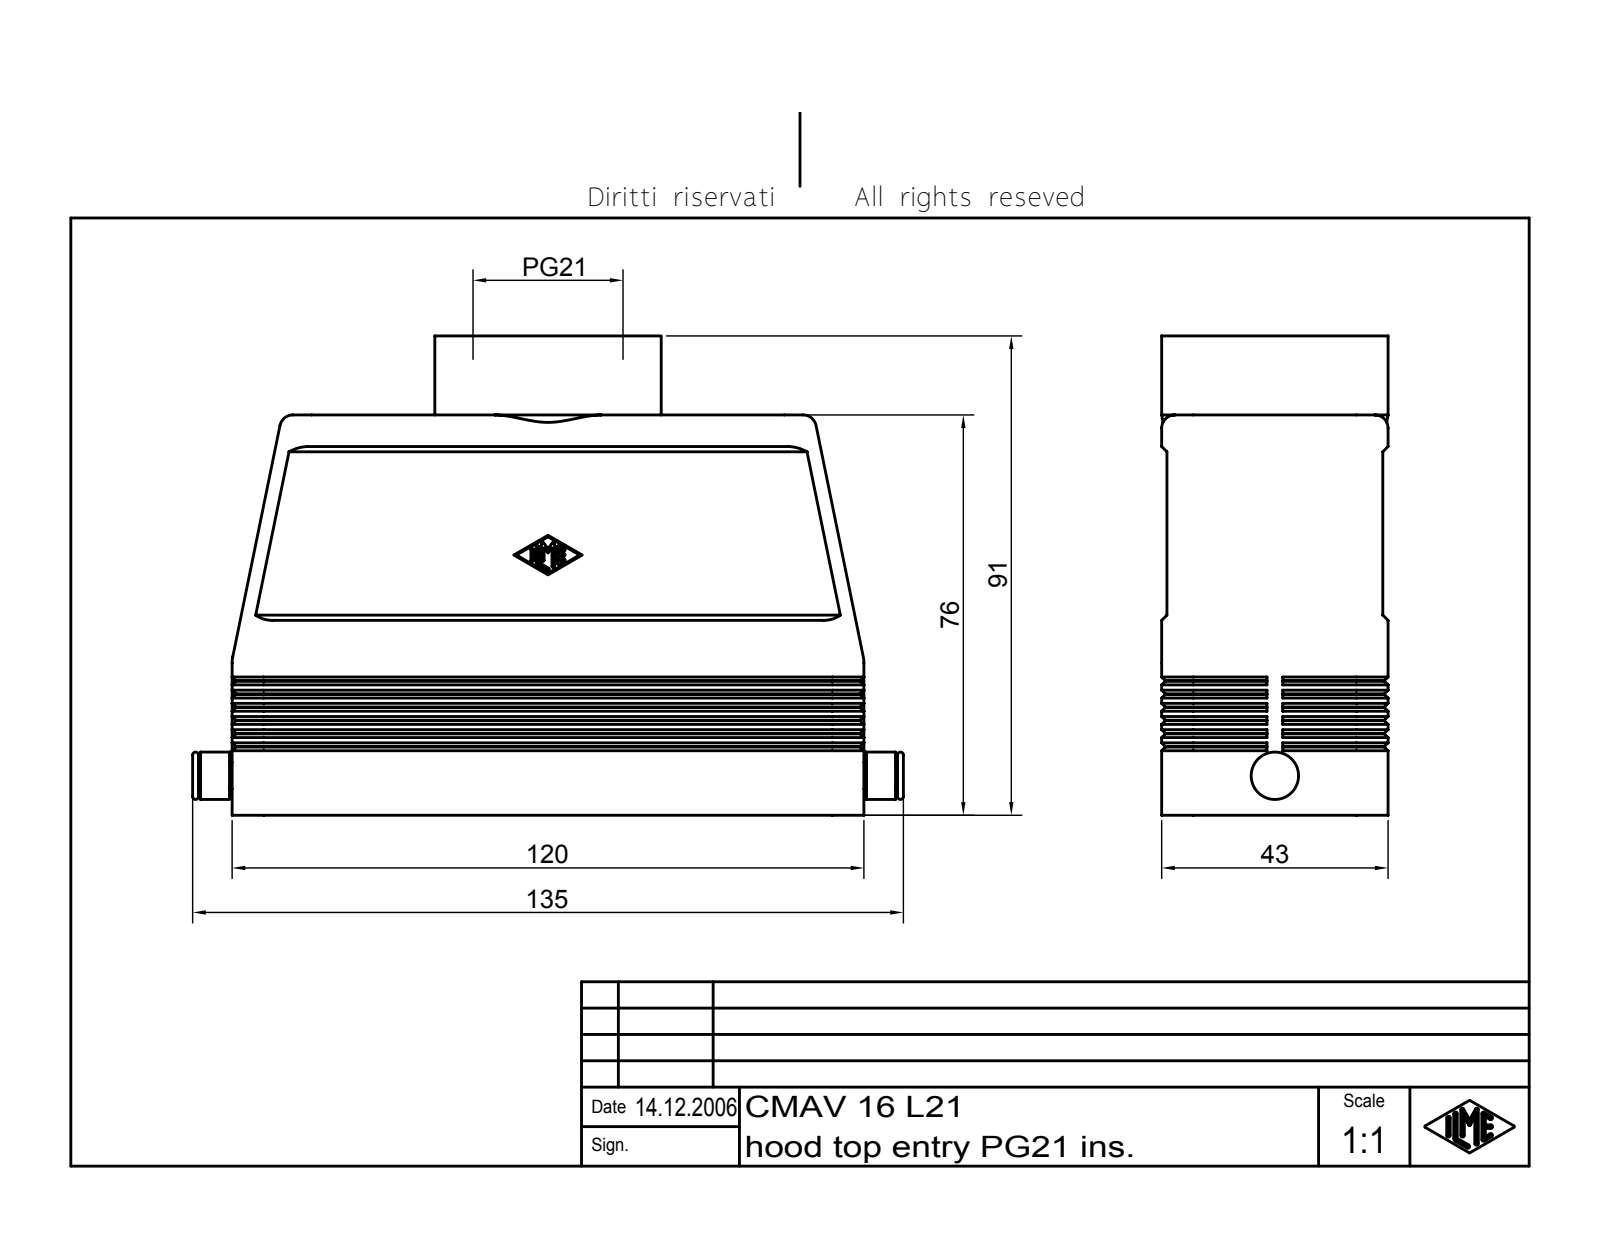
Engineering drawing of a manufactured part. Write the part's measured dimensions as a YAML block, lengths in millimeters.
part_name: "CH Tüllengehäuse für einen Einsatz Teil 6"
step_written_by: "Autodesk Inventor 7 (AUTOMOTIVE_DESIGN)"
units: millimeters
bodies: {solids: 1, faces: 525, planar: 193, cylindrical: 130, other: 202}
overall_size: [135, 91, 43]
volume: 96883
surface_area: 57879
round_holes:
  - {diameter: 24.78, count: 1}
  - {diameter: 26.78, count: 1}
round_bosses_or_shafts:
  - {diameter: 43, count: 1}
  - {diameter: 25.78, count: 1}
  - {diameter: 9, count: 1}
  - {diameter: 5, count: 1}
partial_cylinders:
  - {radius: 0.25, count: 14}
  - {radius: 6, count: 10}
  - {radius: 2, count: 4}
  - {radius: 2.5, count: 4}
  - {radius: 3, count: 4}
  - {radius: 5.3, count: 2}
face_to_face_distances: [3, 37, 40, 1, 2, 42, 39, 43, 41, 9]
